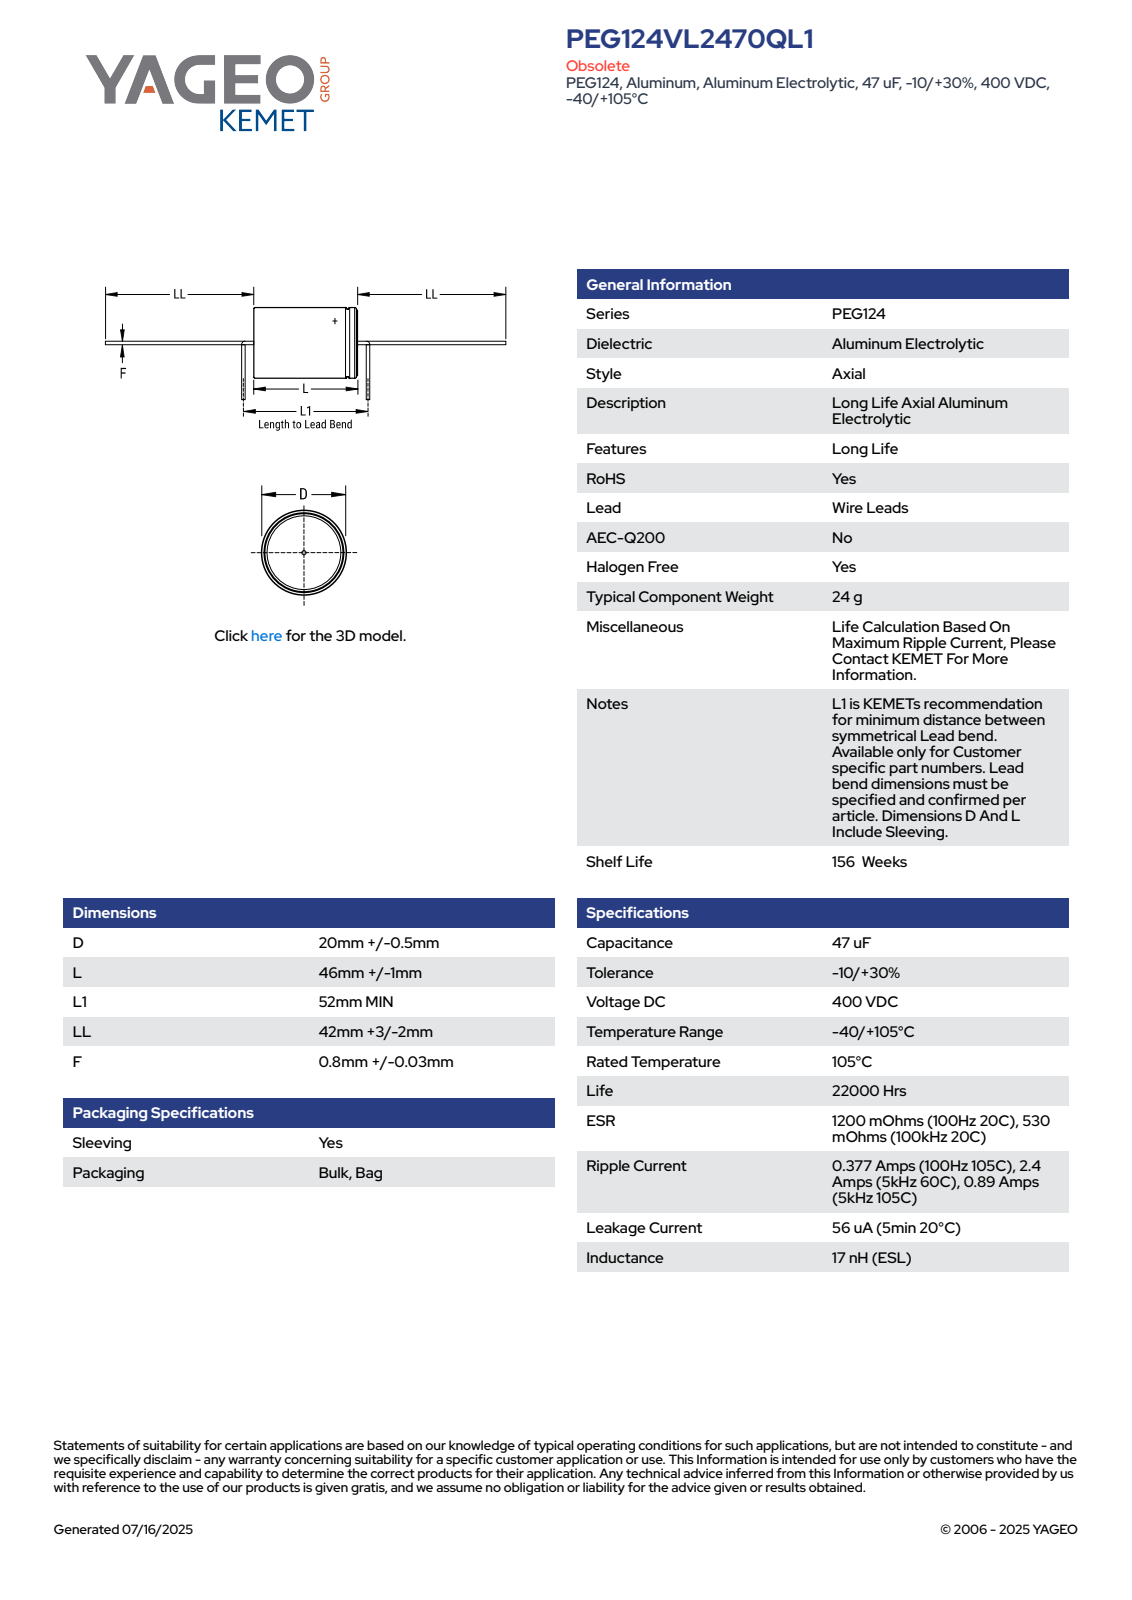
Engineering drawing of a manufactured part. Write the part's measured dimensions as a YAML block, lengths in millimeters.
part_name: "CAA_PEG124_20X46_D20.5L47LL45F0.83"
step_written_by: "SolidWorks 2014 (AUTOMOTIVE_DESIGN)"
units: millimeters
bodies: {solids: 1, faces: 99, planar: 27, cylindrical: 29, other: 43}
overall_size: [134, 20.5, 20.5]
volume: 15252
surface_area: 3982
round_holes:
  - {diameter: 19.5, count: 1}
round_bosses_or_shafts:
  - {diameter: 20.5, count: 1}
  - {diameter: 20, count: 1}
  - {diameter: 0.83, count: 1}
partial_cylinders:
  - {radius: 10.24, count: 1}
face_to_face_distances: [46, 47, 1, 45, 91, 92, 134, 89, 43, 42]
